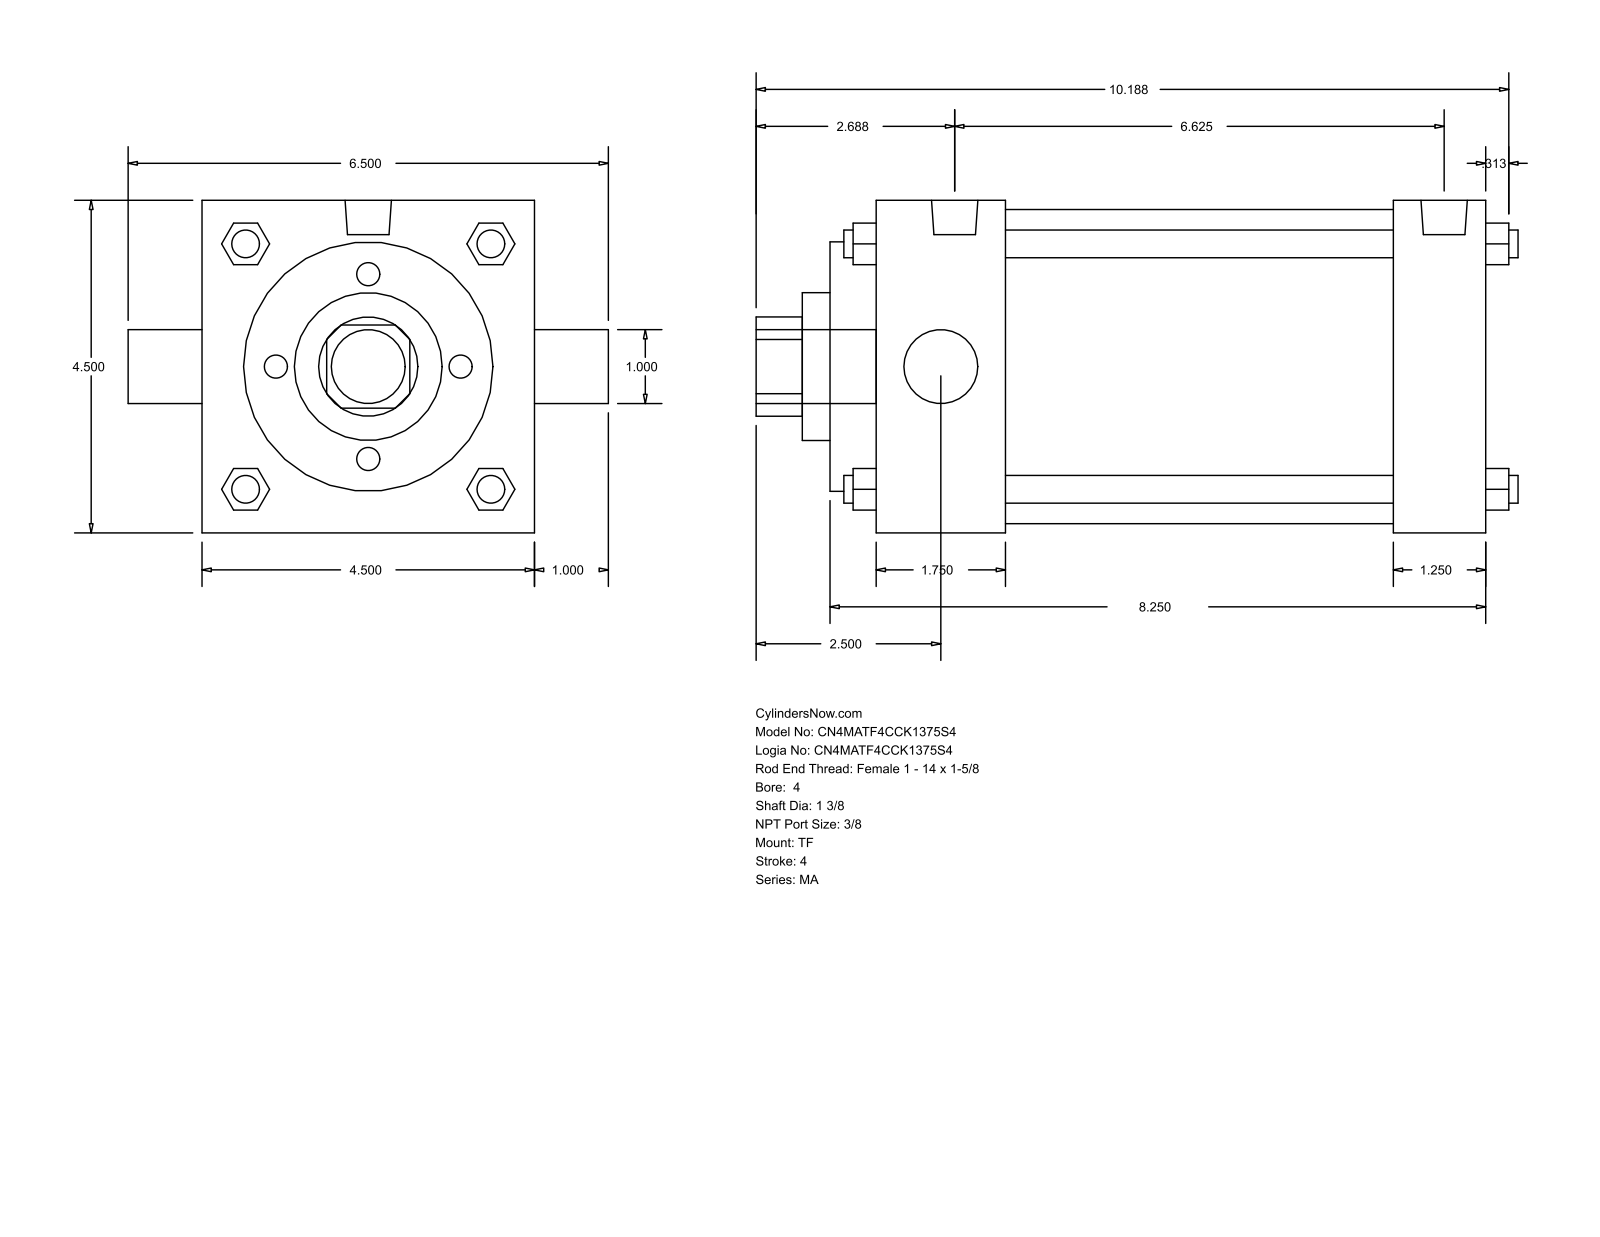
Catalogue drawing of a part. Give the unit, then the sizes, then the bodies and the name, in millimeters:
Units: millimetres
Overall size (bounding box): 261.94 × 165.1 × 114.3
Round holes (diameter × count): ⌀25.4 ×1, ⌀34.92 ×1, ⌀50.8 ×1, ⌀85.72 ×1, ⌀107.95 ×1
Round bosses / shafts (diameter × count): ⌀9.53 ×4, ⌀11.11 ×3, ⌀15.93 ×2, ⌀25.4 ×1
Partial cylindrical surfaces — rounded edges, fillets, slot ends (radius × count): R17.06 ×1
Main face-to-face distances: 114.3, 209.55, 225.42, 165.1, 15.87, 193.67, 177.8, 31.75, 60.32, 44.45
Bodies: 0 solids, 122 faces (93 planar, 29 cylindrical, 0 other)
Part name (STEP PRODUCT): MA_TF__0400_1.375
STEP written by: GSSL Pune (CONFIG_CONTROL_DESIGN)
